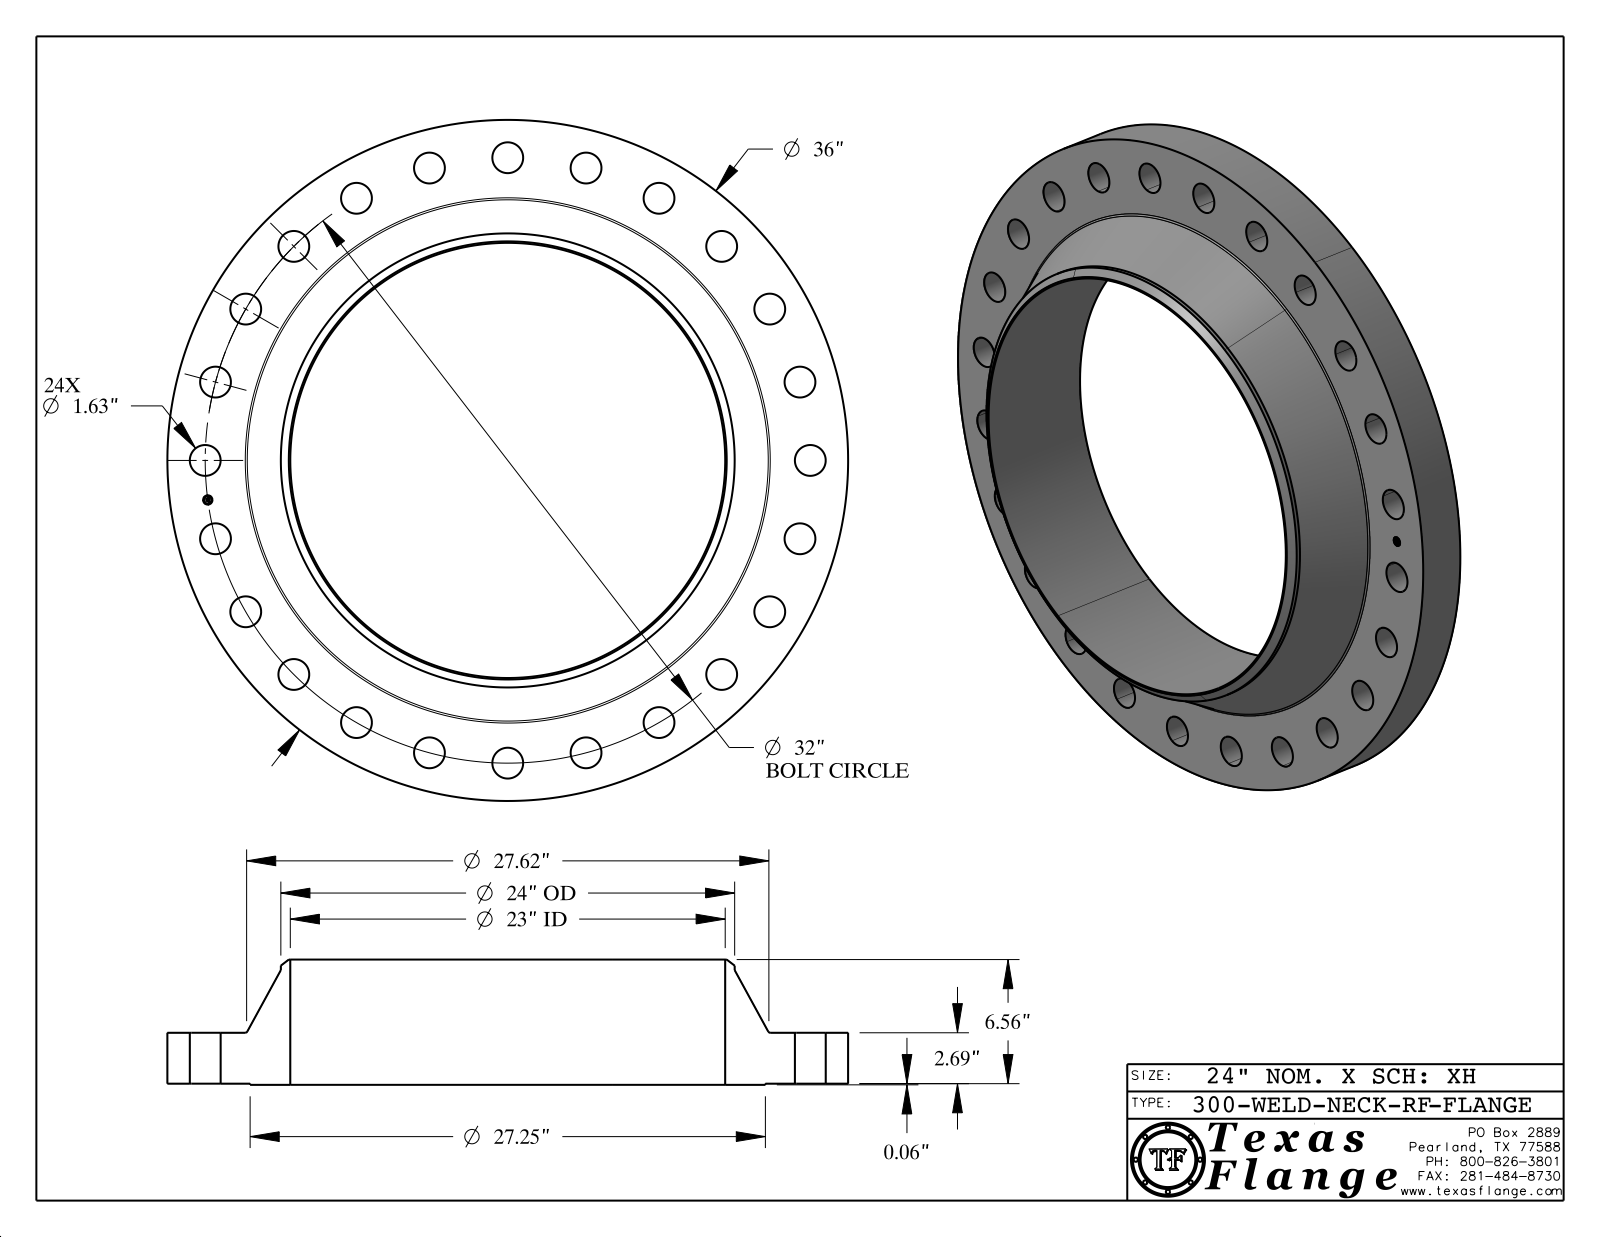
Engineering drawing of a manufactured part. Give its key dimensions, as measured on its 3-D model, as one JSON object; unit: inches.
{"part_name": "300-WELD-NECK-RF", "step_written_by": "CATIA V5 STEP AP214 (AUTOMOTIVE_DESIGN)", "units": "inches", "bodies": {"solids": 1, "faces": 451, "planar": 369, "cylindrical": 76, "other": 6}, "overall_size": [36, 36, 6.623], "volume_in3": 1871, "surface_area_in2": 2407, "round_holes": [[1.63, 24], [0.495, 1], [23, 1]], "round_bosses_or_shafts": [[0.03, 8], [36, 1], [27.25, 1], [24, 1], [0.39, 1]], "face_to_face_distances": [2.69, 0.063, 2.753, 6.622, 6.56, 3.87, 2.738, 2.675, 0.015, 3.885], "hole_center_spacings": [16, 30.909, 4.177, 8.282, 12.246, 19.48, 22.627, 25.387]}
